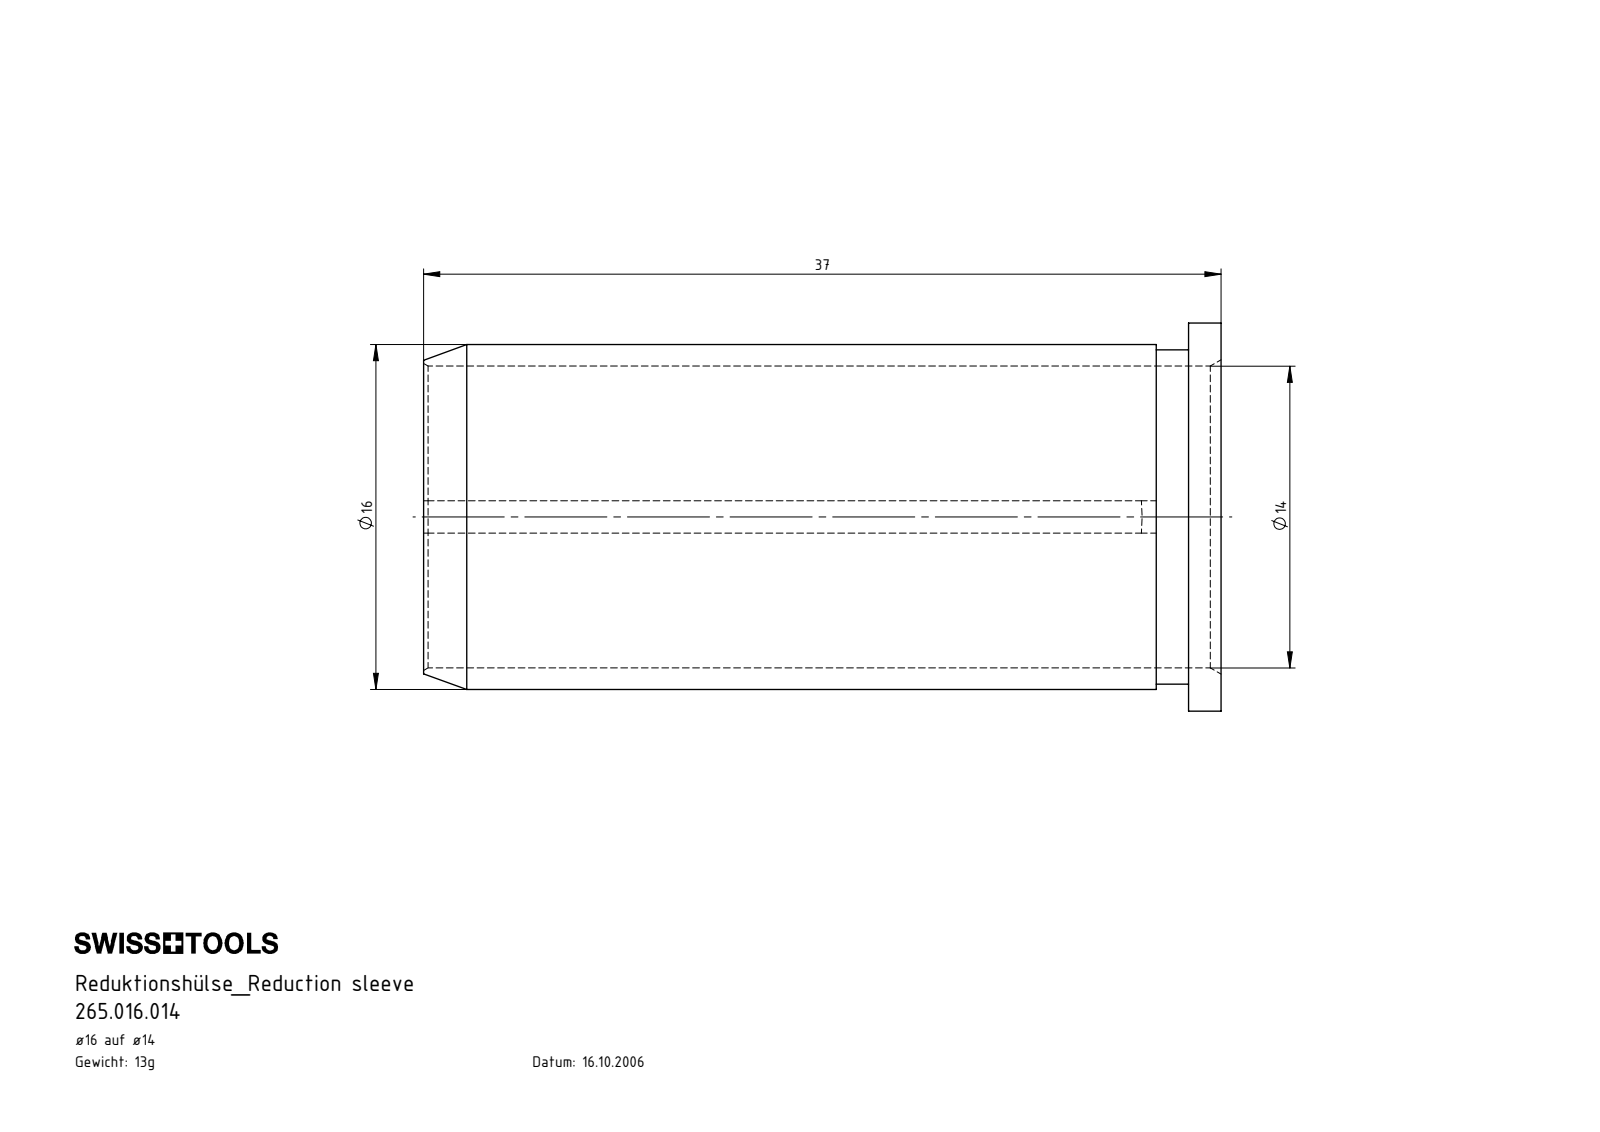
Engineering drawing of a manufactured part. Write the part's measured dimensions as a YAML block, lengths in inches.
part_name: "U14-U16.001.037_A"
step_written_by: "SolidWorks 2012 (CONFIG_CONTROL_DESIGN)"
units: inches
bodies: {solids: 1, faces: 24, planar: 6, cylindrical: 10, other: 8}
overall_size: [1.457, 0.709, 0.709]
volume: 0.105
surface_area: 5.642
round_holes:
  - {diameter: 0.551, count: 1}
round_bosses_or_shafts:
  - {diameter: 0.709, count: 1}
  - {diameter: 0.63, count: 1}
  - {diameter: 0.61, count: 1}
partial_cylinders:
  - {radius: 1.24, count: 1}
face_to_face_distances: [0.059, 0.118, 1.339, 1.398, 1.457]
